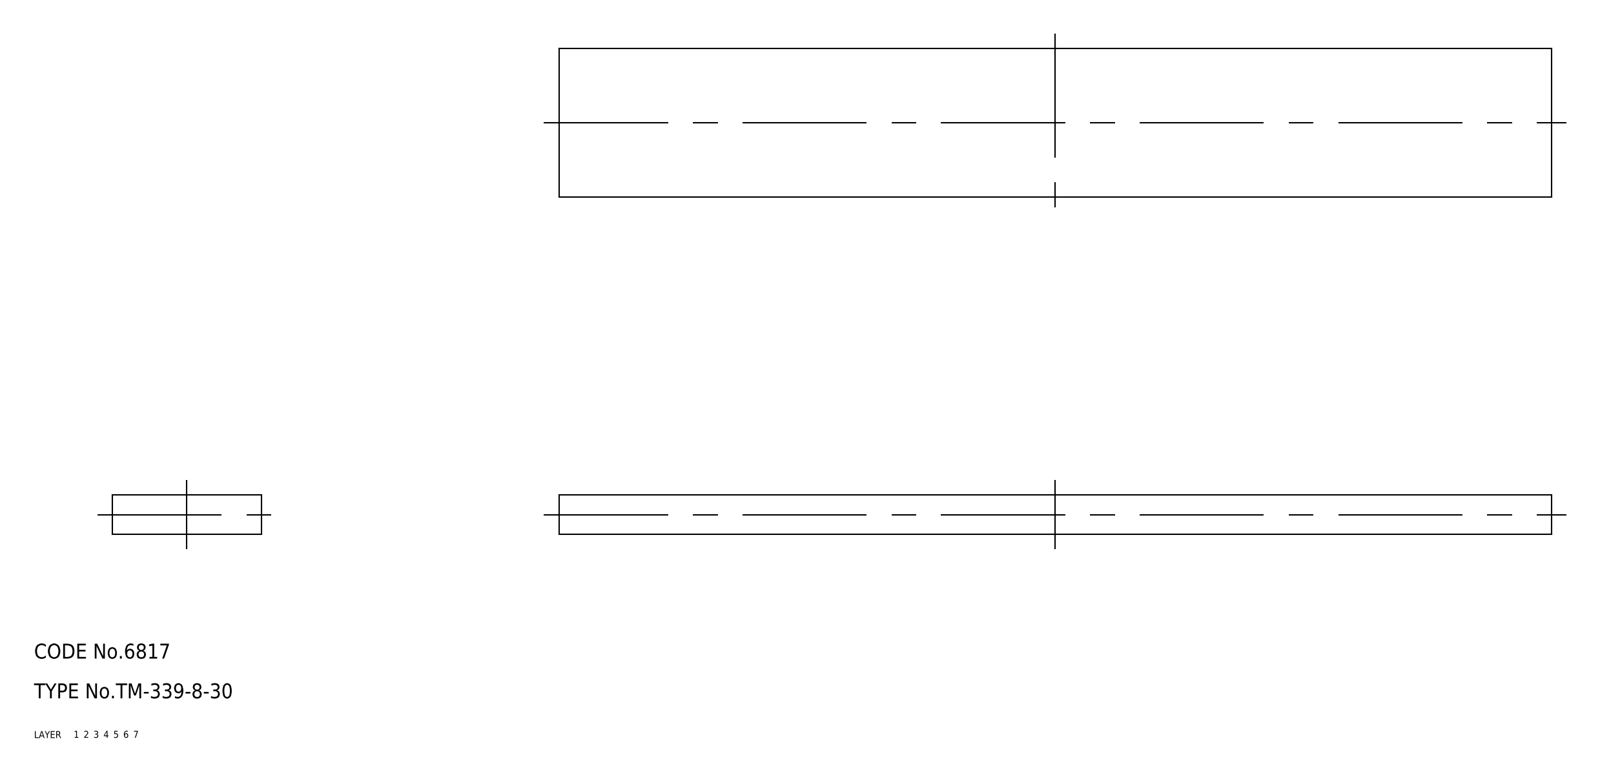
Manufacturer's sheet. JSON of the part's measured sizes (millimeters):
{"part_name": "rubber foam", "step_written_by": "CADfix (AUTOMOTIVE_DESIGN)", "units": "millimeters", "bodies": {"solids": 1, "faces": 6, "planar": 0, "cylindrical": 0, "other": 6}, "overall_size": [200, 30, 8], "volume_mm3": 48000, "surface_area_mm2": 15680}
